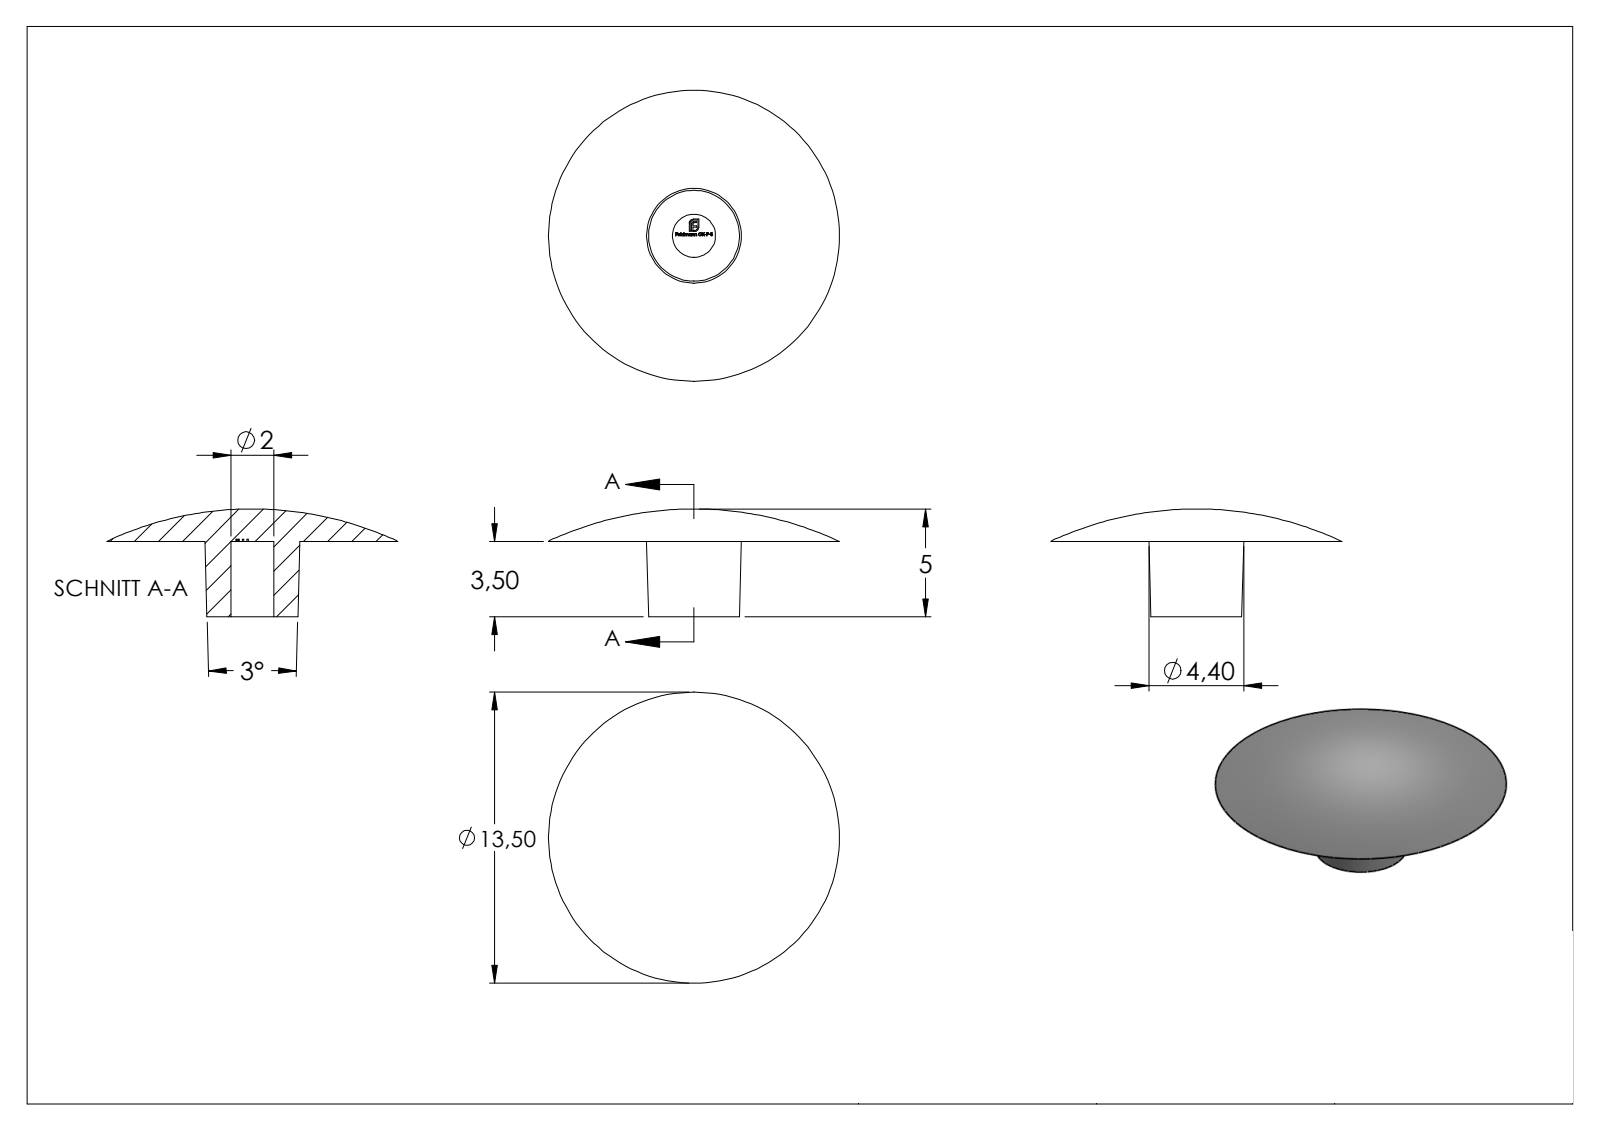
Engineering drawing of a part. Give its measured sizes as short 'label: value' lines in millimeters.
name: GK-P-S
written by: SolidWorks 2018 (CONFIG_CONTROL_DESIGN)
unit: mm
bodies: 1 solid, 232 faces (131 planar, 1 cylindrical, 100 other)
size: 13.5 × 13.5 × 5
volume: 149 mm³; area: 363 mm²
holes: 1× ⌀2
face distances: 3.5, 3.6, 0.4, 0.34, 0.72, 0.49, 0.38, 0.53, 0.73, 0.57
